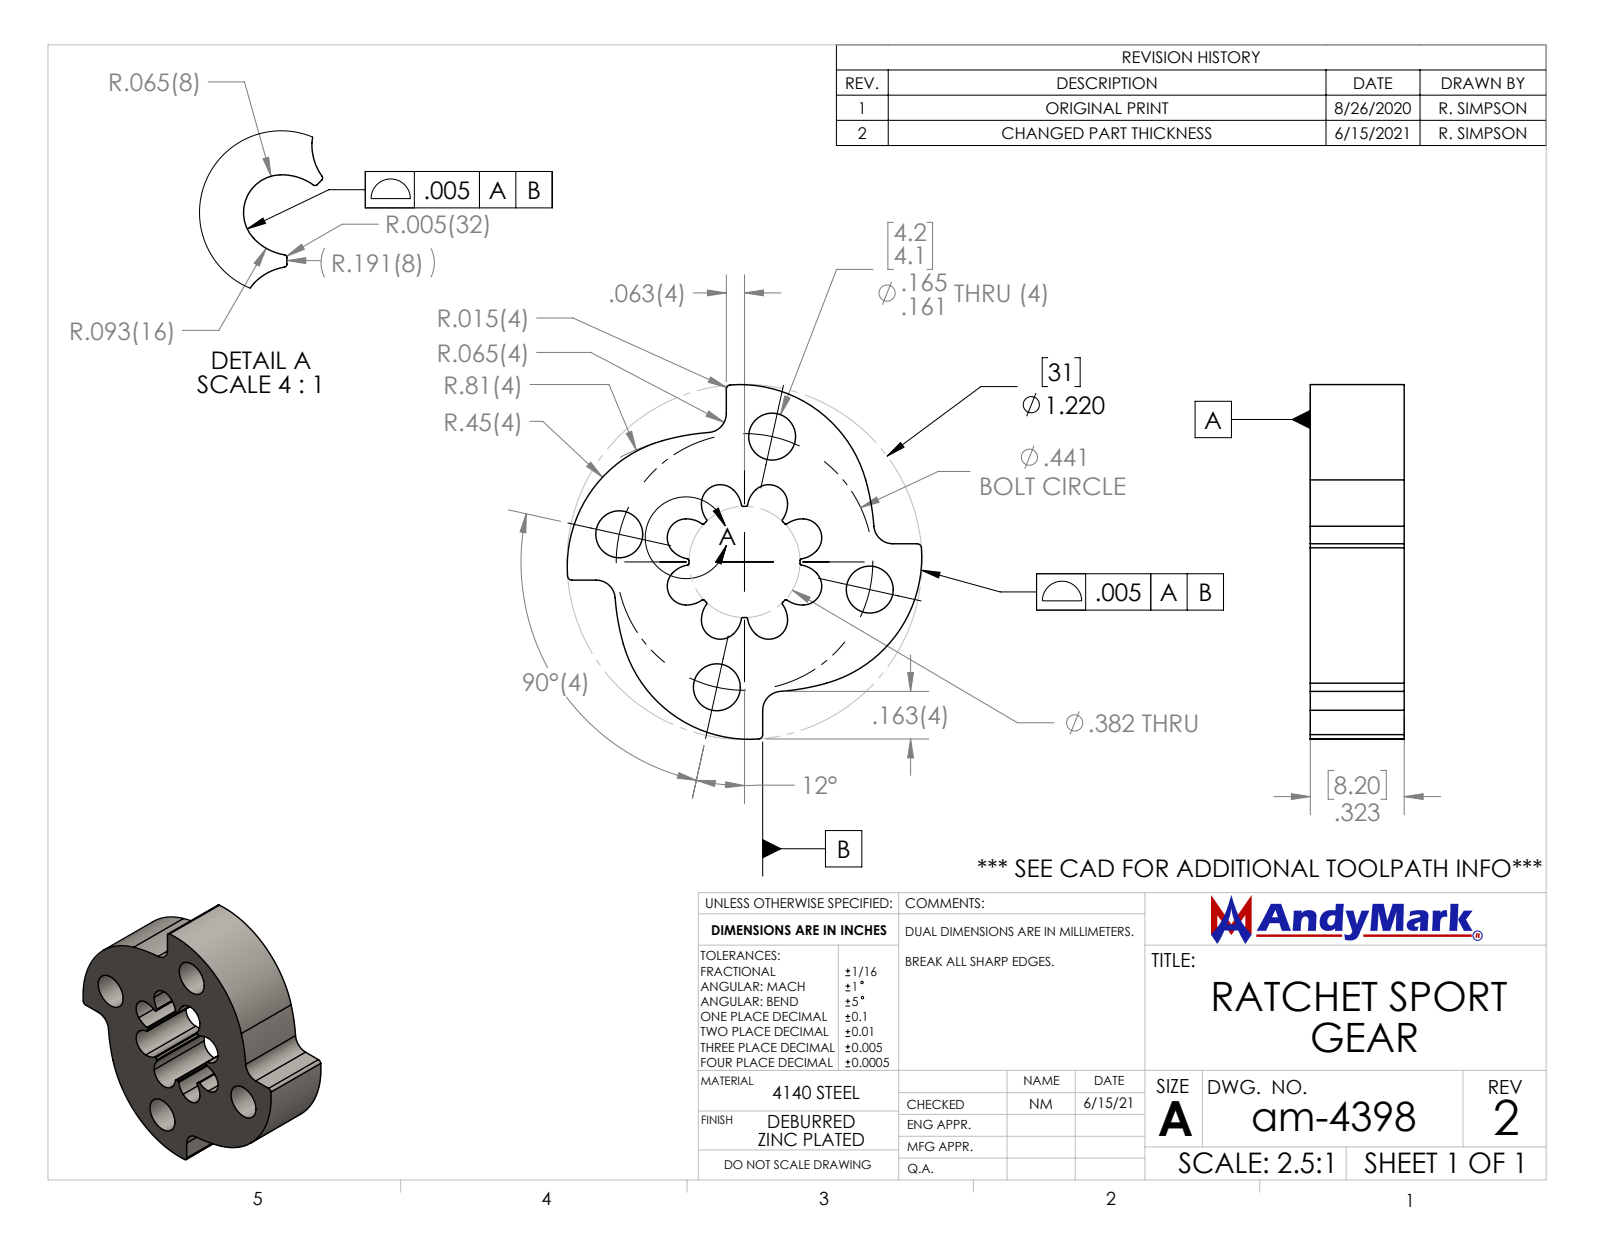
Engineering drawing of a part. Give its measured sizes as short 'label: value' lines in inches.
name: am-4398 Ratchet Sport Gear
written by: SolidWorks 2021 (AUTOMOTIVE_DESIGN)
unit: in
bodies: 1 solid, 88 faces (6 planar, 82 cylindrical, 0 other)
size: 1.219 × 1.219 × 0.323
volume: 0.211 in³; area: 3.993 in²
holes: 4× ⌀0.161
rounds: 16× R0.005, 16× R0.093, 8× R0.065, 4× R0.015, 4× R0.065, 4× R0.45, 4× R0.806, 1× R0.191
face distances: 0.323, 0.125, 0.125
hole spacings: 0.624, 0.881, 0.882
